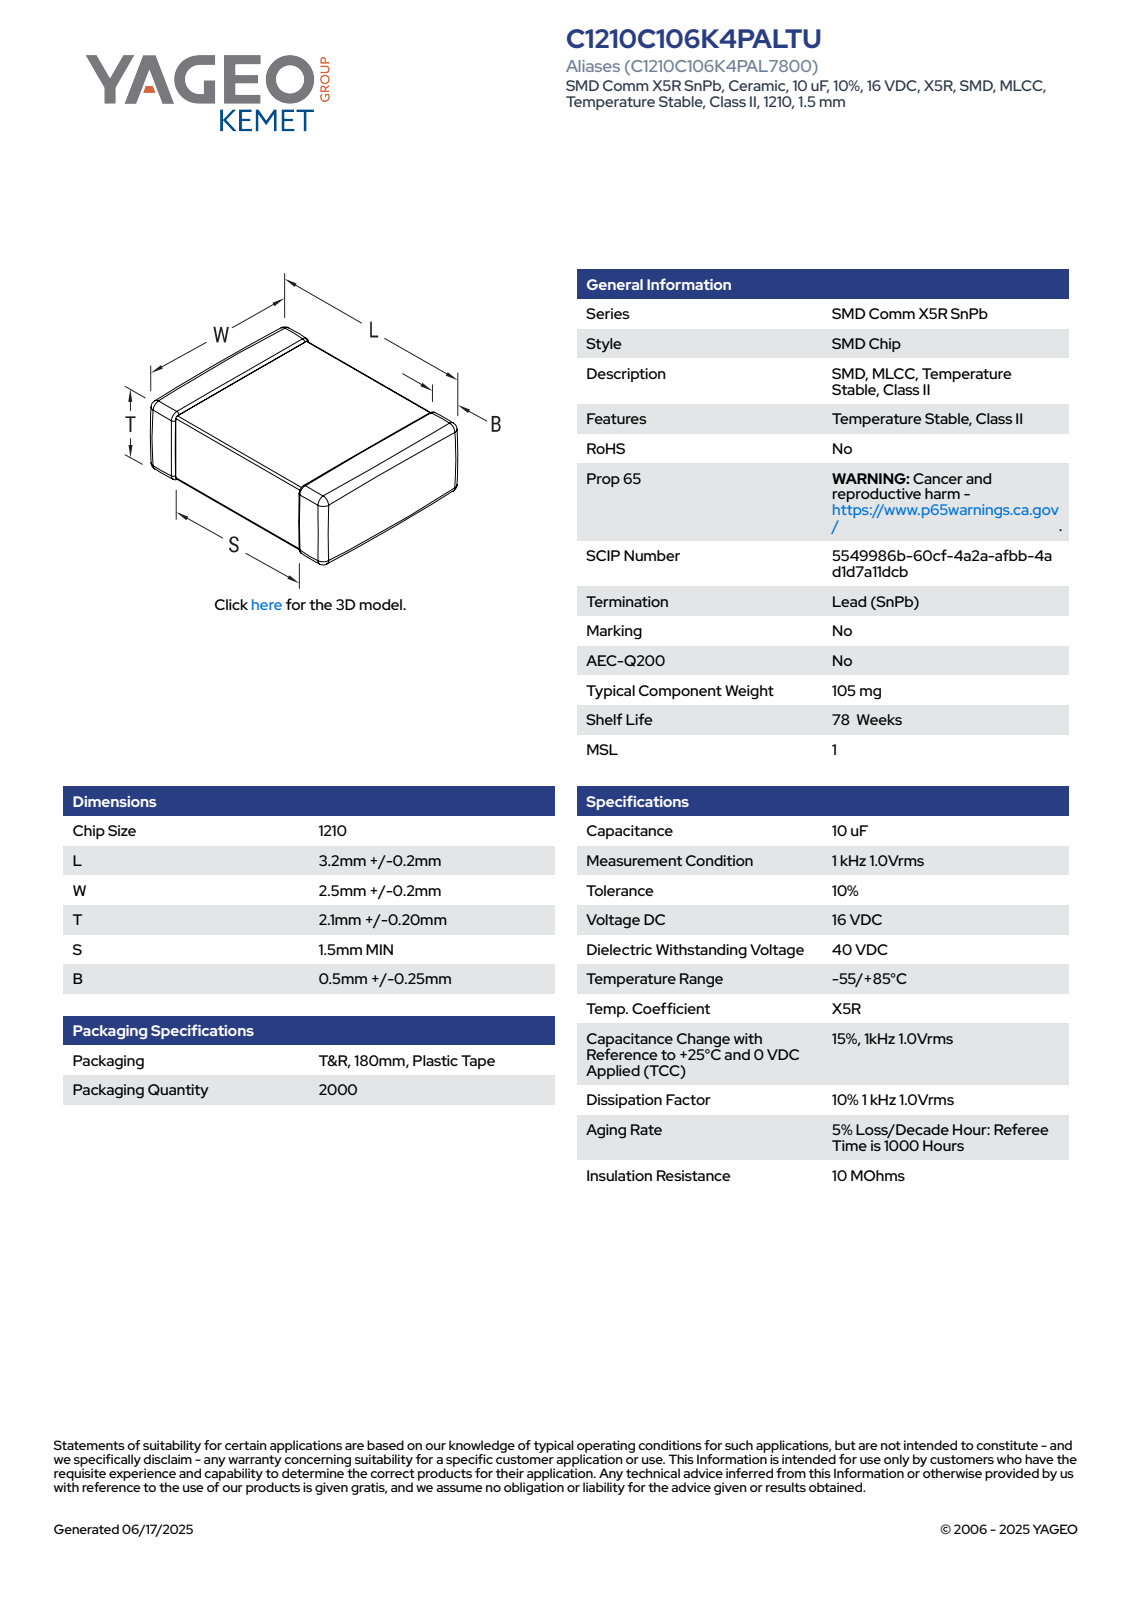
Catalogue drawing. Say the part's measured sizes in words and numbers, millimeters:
The part is named "CCS_CCSTD_1210_L3.4W2.7T2.3B0.5". Its 3-D file was written by "SolidWorks 2021 (AUTOMOTIVE_DESIGN)". It is 4 solids with 125 faces: 71 planar, 38 cylindrical and 16 other. Overall it measures 3.4 by 2.7 by 2.3 millimeters. Its volume is 20 cubic millimeters and its surface area 46 square millimeters. The main face-to-face distances are 2.24, 3.4, 2.64, 2.18, 2.58, 2.3, 2.7, 2.25, 2.19, 0.4.
